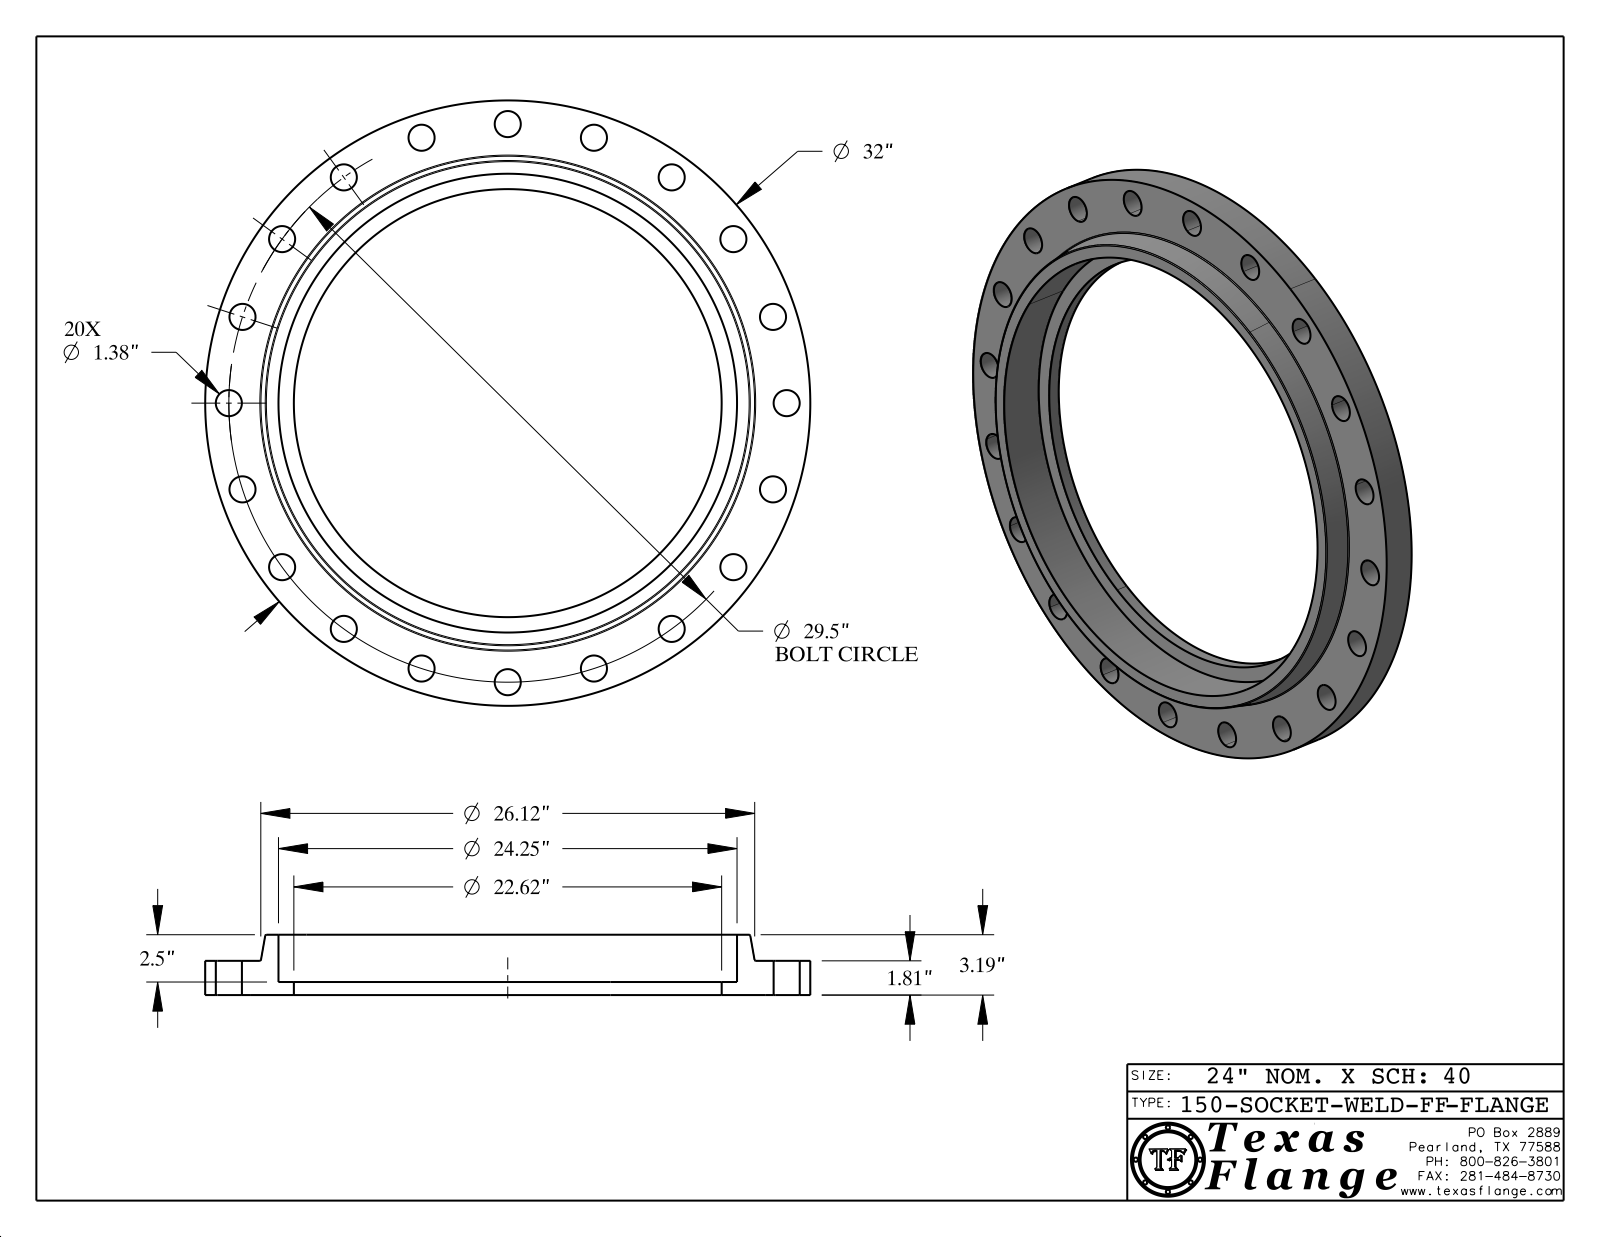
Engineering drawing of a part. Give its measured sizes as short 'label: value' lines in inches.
name: 150-SOCKET-WELD-FF
written by: CATIA V5 STEP AP214 (AUTOMOTIVE_DESIGN)
unit: in
bodies: 1 solid, 442 faces (370 planar, 66 cylindrical, 6 other)
size: 32 × 32 × 3.19
volume: 695.3 in³; area: 1 415 in²
holes: 20× ⌀1.38, 1× ⌀0.495, 1× ⌀22.624, 1× ⌀24.25
bosses: 8× ⌀0.03, 1× ⌀32, 1× ⌀0.39
face distances: 1.81, 0.69, 1.12, 3.19, 2.5, 1.38, 1.795, 1.105, 0.015, 1.395
hole spacings: 14.75, 29.137, 4.615, 17.34, 20.859, 23.866, 26.285, 9.116
